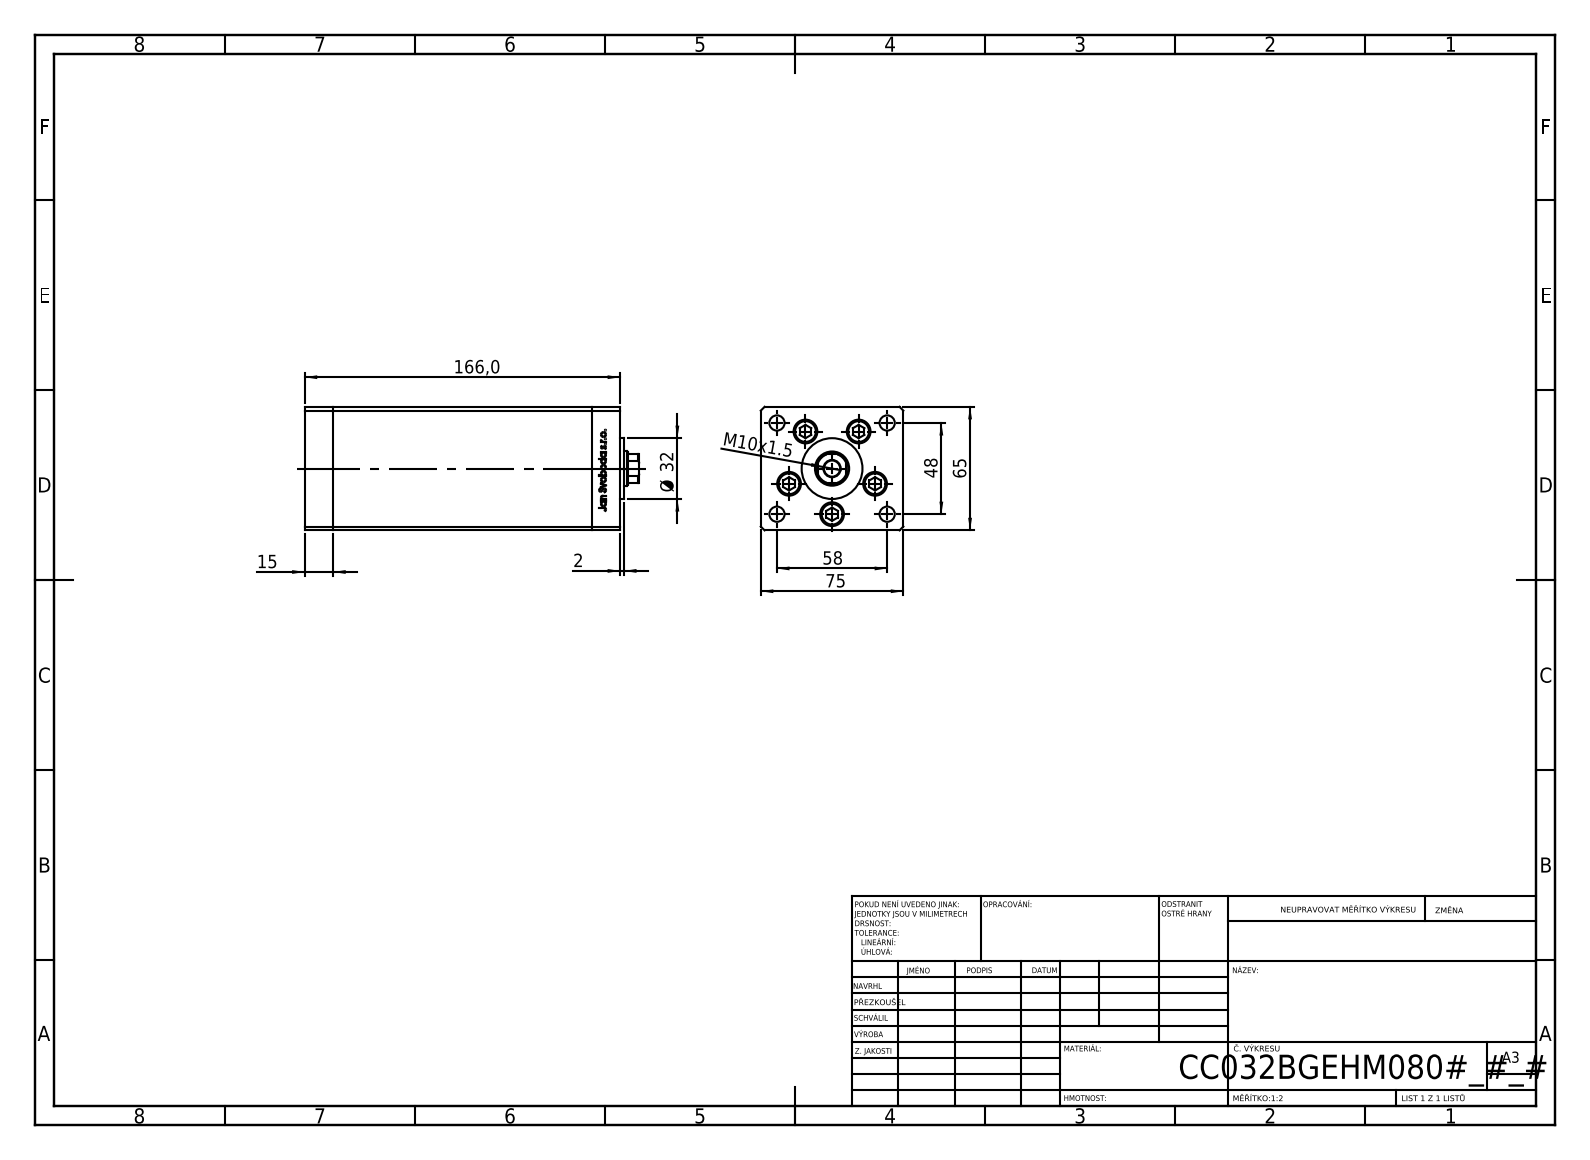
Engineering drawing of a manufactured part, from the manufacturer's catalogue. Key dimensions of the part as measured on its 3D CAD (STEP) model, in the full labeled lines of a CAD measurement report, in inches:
Part name (STEP PRODUCT): ALLEN BOLT; V220C_FRONT_B; V220C_B MIDDLE; V220C BACK_B (+1 more)
STEP written by: SolidWorks 2019 (CONFIG_CONTROL_DESIGN)
Units: inches
Bodies: 14 solids, 1183 faces (462 planar, 147 cylindrical, 574 other)
Overall size (bounding box): 6.929 × 2.953 × 2.559
Volume: 44.09 in³ · Surface area: 197.4 in²
Round holes (diameter × count): ⌀0.354 ×5, ⌀0.492 ×5, ⌀0.315 ×4, ⌀0.079 ×2, ⌀0.518 ×2, ⌀0.335 ×1, ⌀0.709 ×1
Round bosses / shafts (diameter × count): ⌀0.315 ×5, ⌀1.26 ×1
Partial cylindrical surfaces — rounded edges, fillets, slot ends (radius × count): R0.037 ×2, R0.335 ×1
Main face-to-face distances: 2.953, 2.559, 0.591, 5.354, 5.945, 6.535, 1.102, 0.512, 2.146, 0.413
Hole centre spacings: 0.945, 1.482, 0.617, 0.678, 1.091, 1.135, 1.142, 1.285
